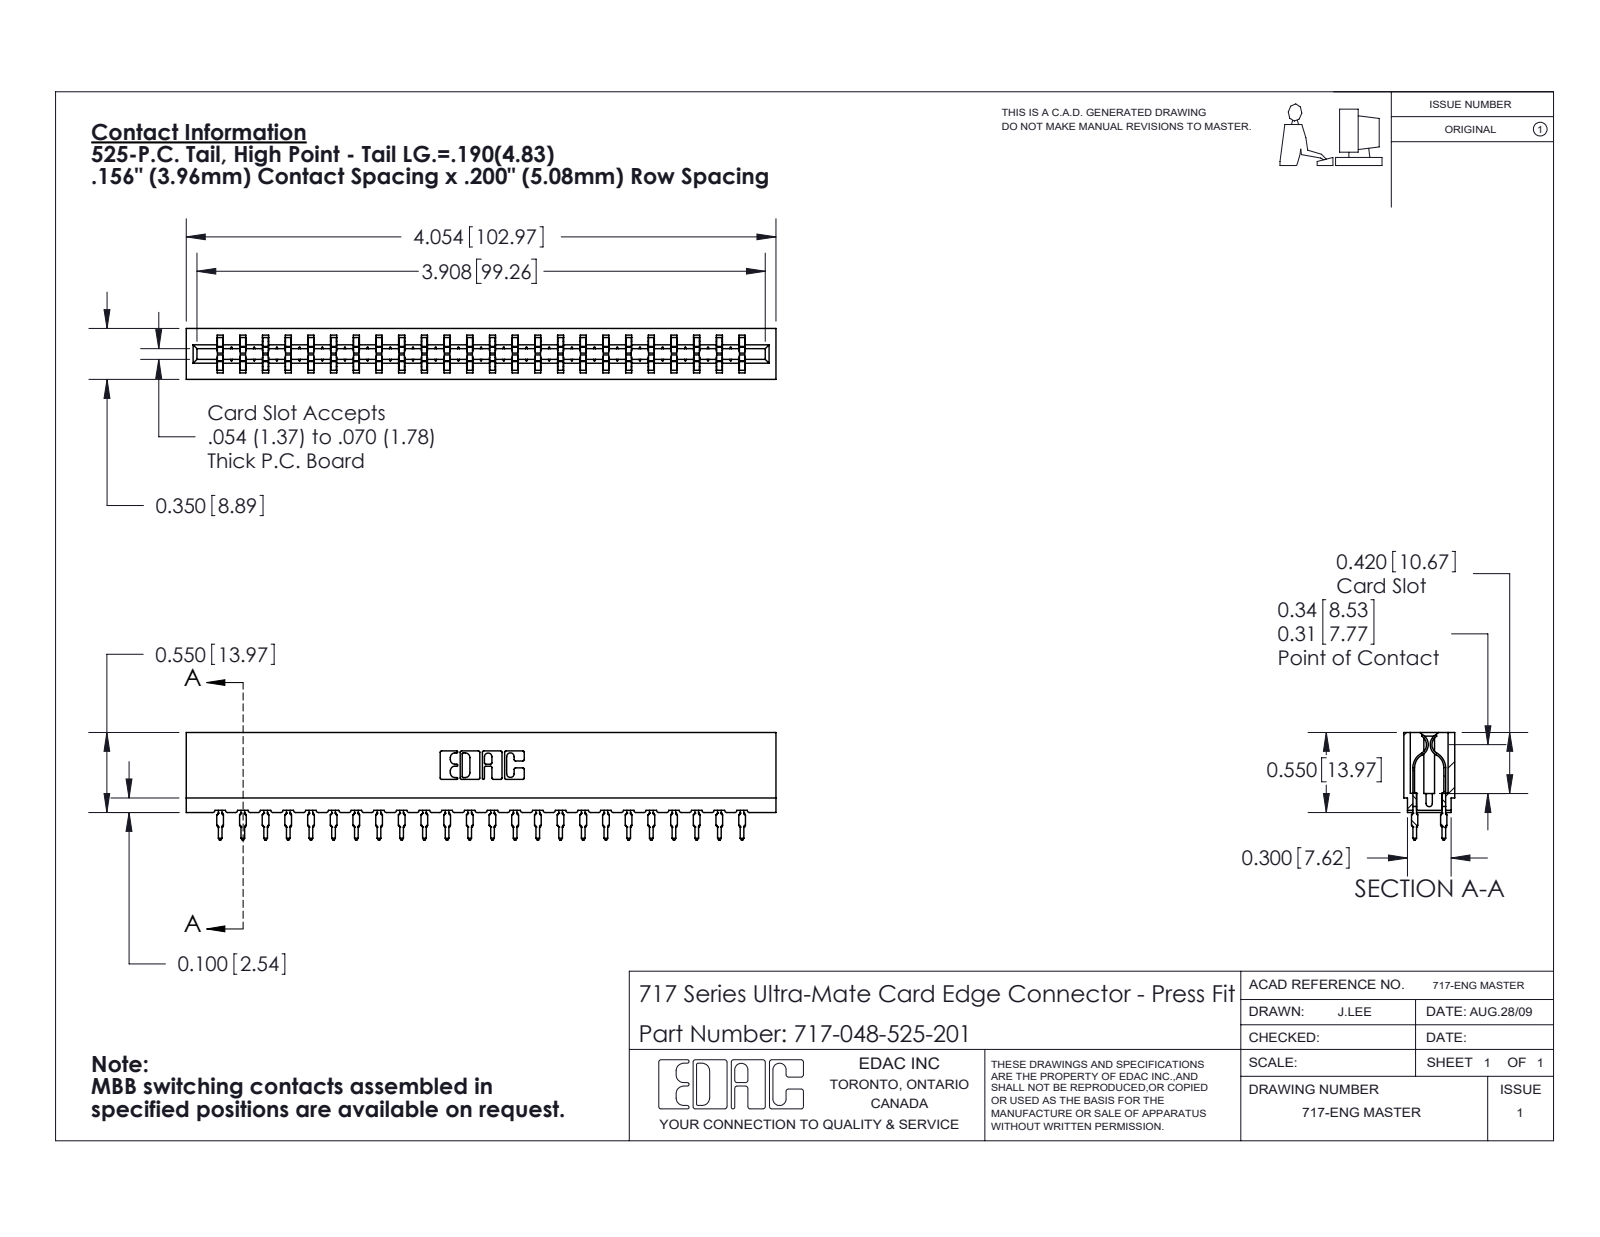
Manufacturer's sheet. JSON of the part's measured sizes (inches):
{"part_name": "717 Part_Insulator Option - 06; 717-048-525-201; 745-292-001_525", "step_written_by": "SolidWorks 2020 (CONFIG_CONTROL_DESIGN)", "units": "inches", "bodies": {"solids": 49, "faces": 4414, "planar": 2286, "cylindrical": 880, "other": 1248}, "overall_size": [4.054, 0.739, 0.35], "volume_in3": 0.548, "surface_area_in2": 20.84, "partial_cylinders_radius": [[0.021, 96], [0.015, 48], [0.01, 22], [0.005, 8], [0.011, 8], [0.007, 6], [0.031, 6], [0.026, 3]], "face_to_face_distances": [0.212, 0.138, 0.35, 0.063, 0.287, 0.076, 0.149, 0.156, 0.074, 0.624]}
